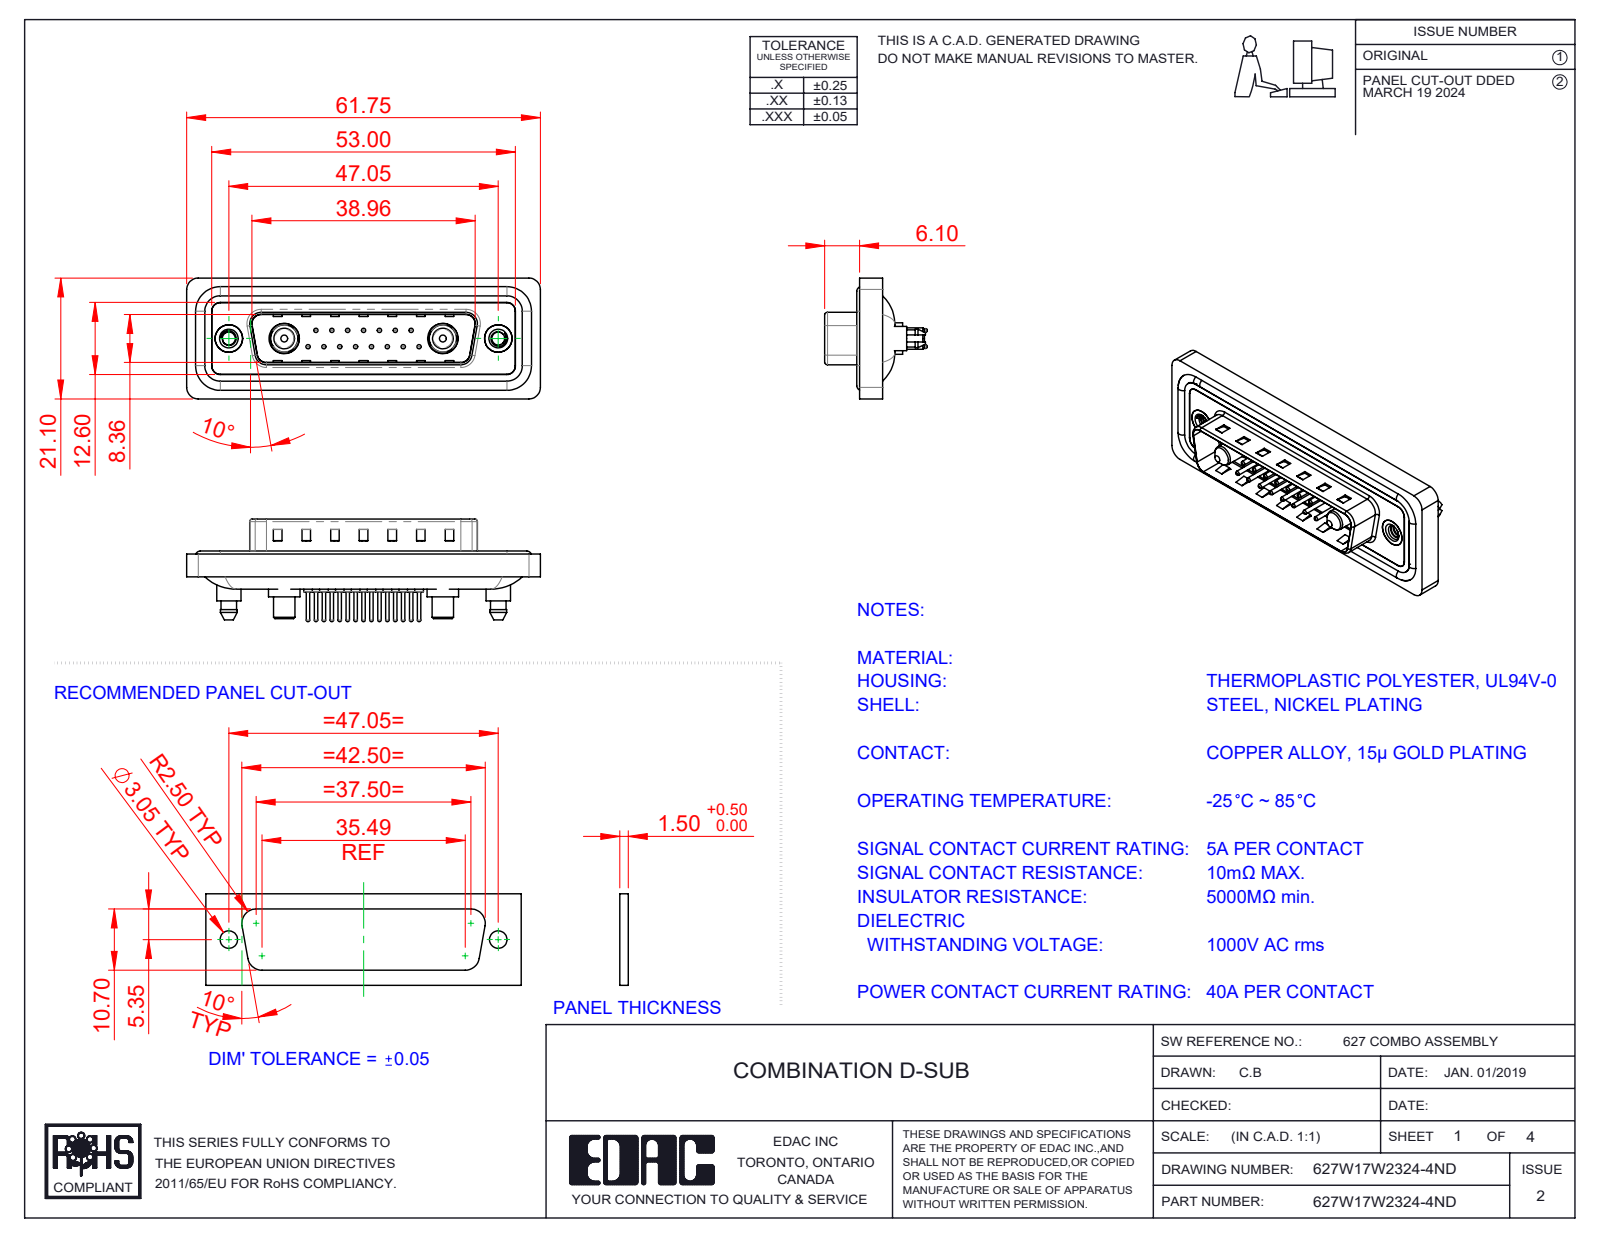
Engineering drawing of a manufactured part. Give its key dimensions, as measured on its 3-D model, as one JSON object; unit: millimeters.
{"part_name": "627Combo Waterproof Housing_25 Contacts; 627Combo Shell Front_25 Contacts; Power Pin_40A S; 627W17W2324-4ND (+6 more)", "step_written_by": "SolidWorks 2023 (CONFIG_CONTROL_DESIGN)", "units": "millimeters", "bodies": {"solids": 26, "faces": 1174, "planar": 350, "cylindrical": 476, "other": 348}, "overall_size": [61.75, 21.1, 17.9], "volume_mm3": 7438, "surface_area_mm2": 12272, "round_holes": [[0.75, 15], [1.6, 15], [2, 15], [2.26, 2], [4, 2], [4.8, 2], [4.85, 2], [5, 2], [5.3, 2]], "round_bosses_or_shafts": [[1.5, 15], [0.6, 15], [1.6, 4], [5.5, 2], [5.4, 2], [5.2, 2], [4.9, 2], [4.75, 2]], "partial_cylinders_radius": [[1.5, 24], [2, 18], [1.6, 10], [0.5, 8], [0.25, 4], [0.6, 4], [0.65, 4], [0.9, 4]], "face_to_face_distances": [0.4, 1.5, 1.1, 1.6, 0.5, 3.1, 2.9, 0.82, 9.58, 4.1], "hole_center_spacings": [3.16, 2.77, 5.54, 8.31, 5.04, 7.49, 11.08, 5.03]}
